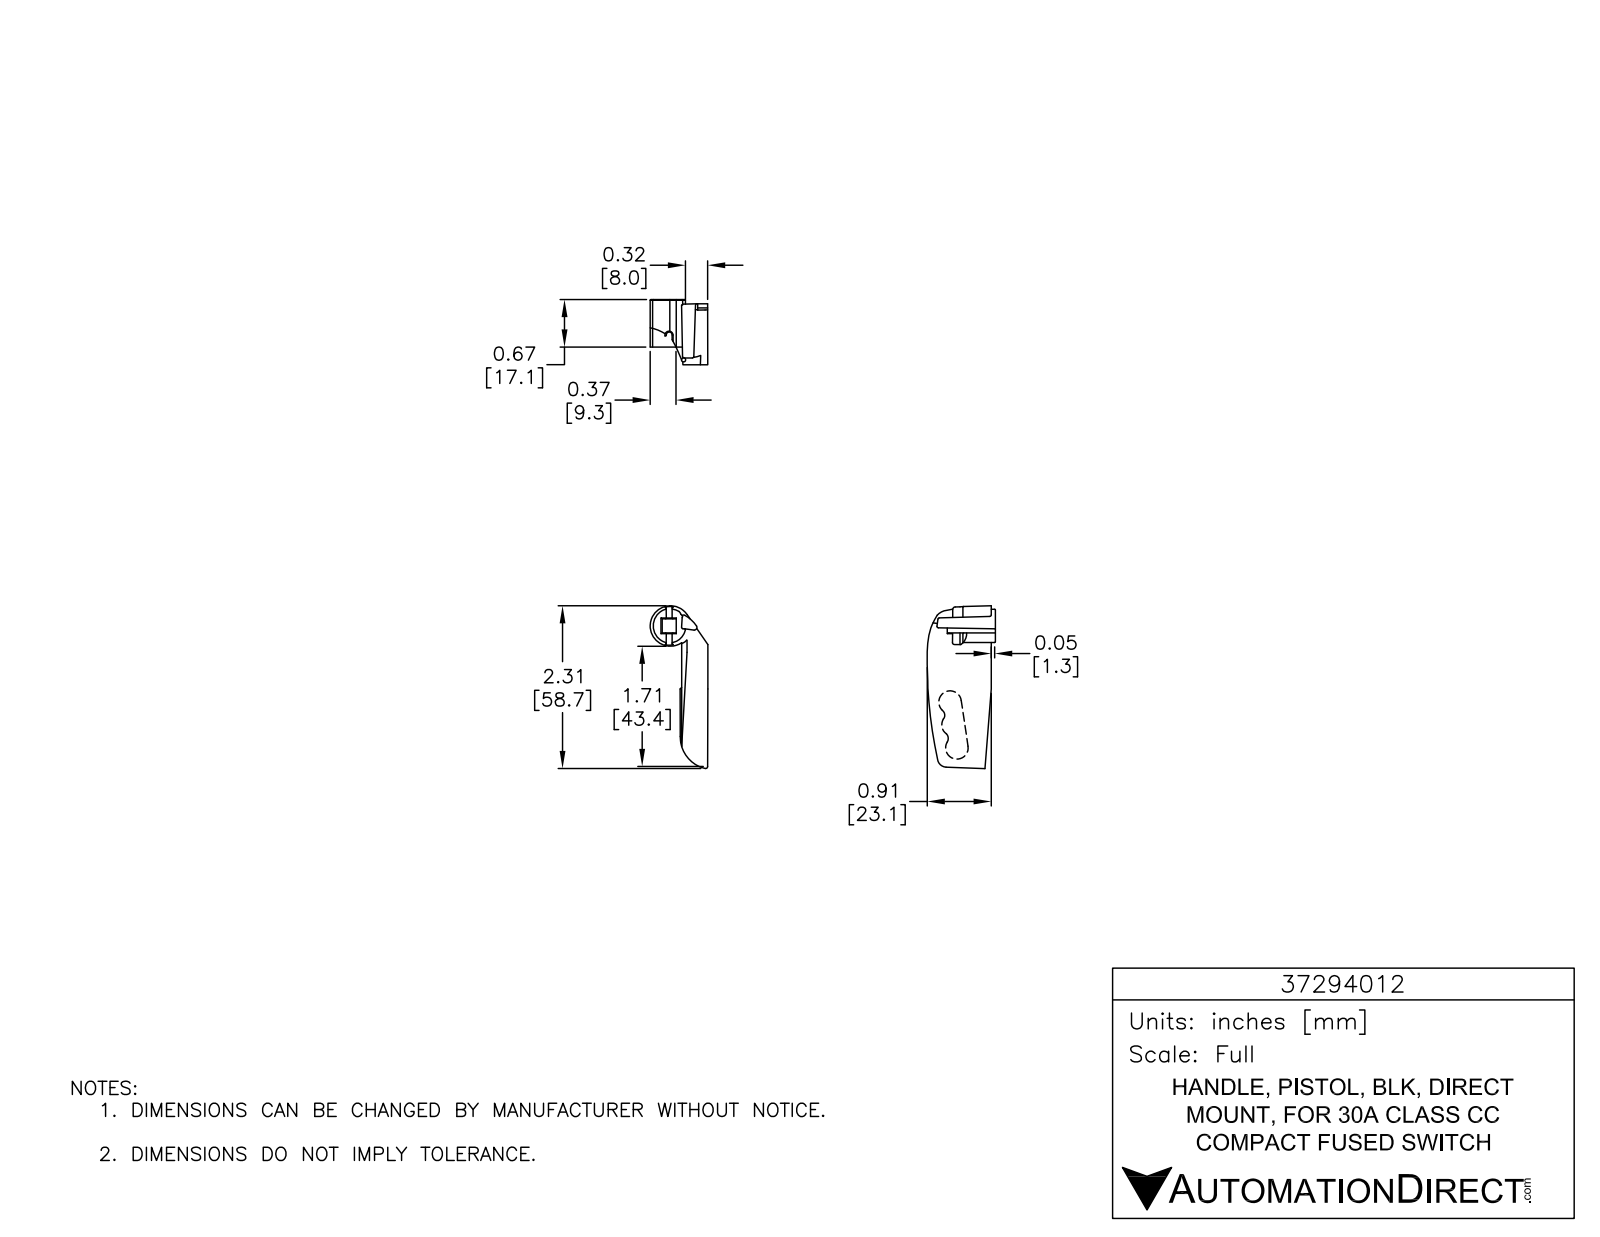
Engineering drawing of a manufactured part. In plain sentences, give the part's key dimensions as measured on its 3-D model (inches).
The part is named "37294012". Its 3-D file was written by "SolidWorks 2015 (AUTOMOTIVE_DESIGN)". It is 3 solids with 110 faces: 66 planar, 30 cylindrical and 14 other. Overall it measures 2.725 by 2.331 by 1.164 inches. Its volume is 1.199 cubic inches and its surface area 24.09 square inches. Round holes: 1 of diameter 0.43. Round bosses or shafts: 1 of diameter 0.475, 1 of diameter 0.4. Partial cylindrical surfaces (rounded edges, fillets, slot ends): 12 of radius 0.02, 5 of radius 0.062, 2 of radius 0.281, 1 of radius 0.295, 1 of radius 0.313, 1 of radius 0.375. The main face-to-face distances are 0.08, 0.08, 0.65, 1.101, 1.164, 0.063, 0.25, 1.69, 0.726, 0.375.
